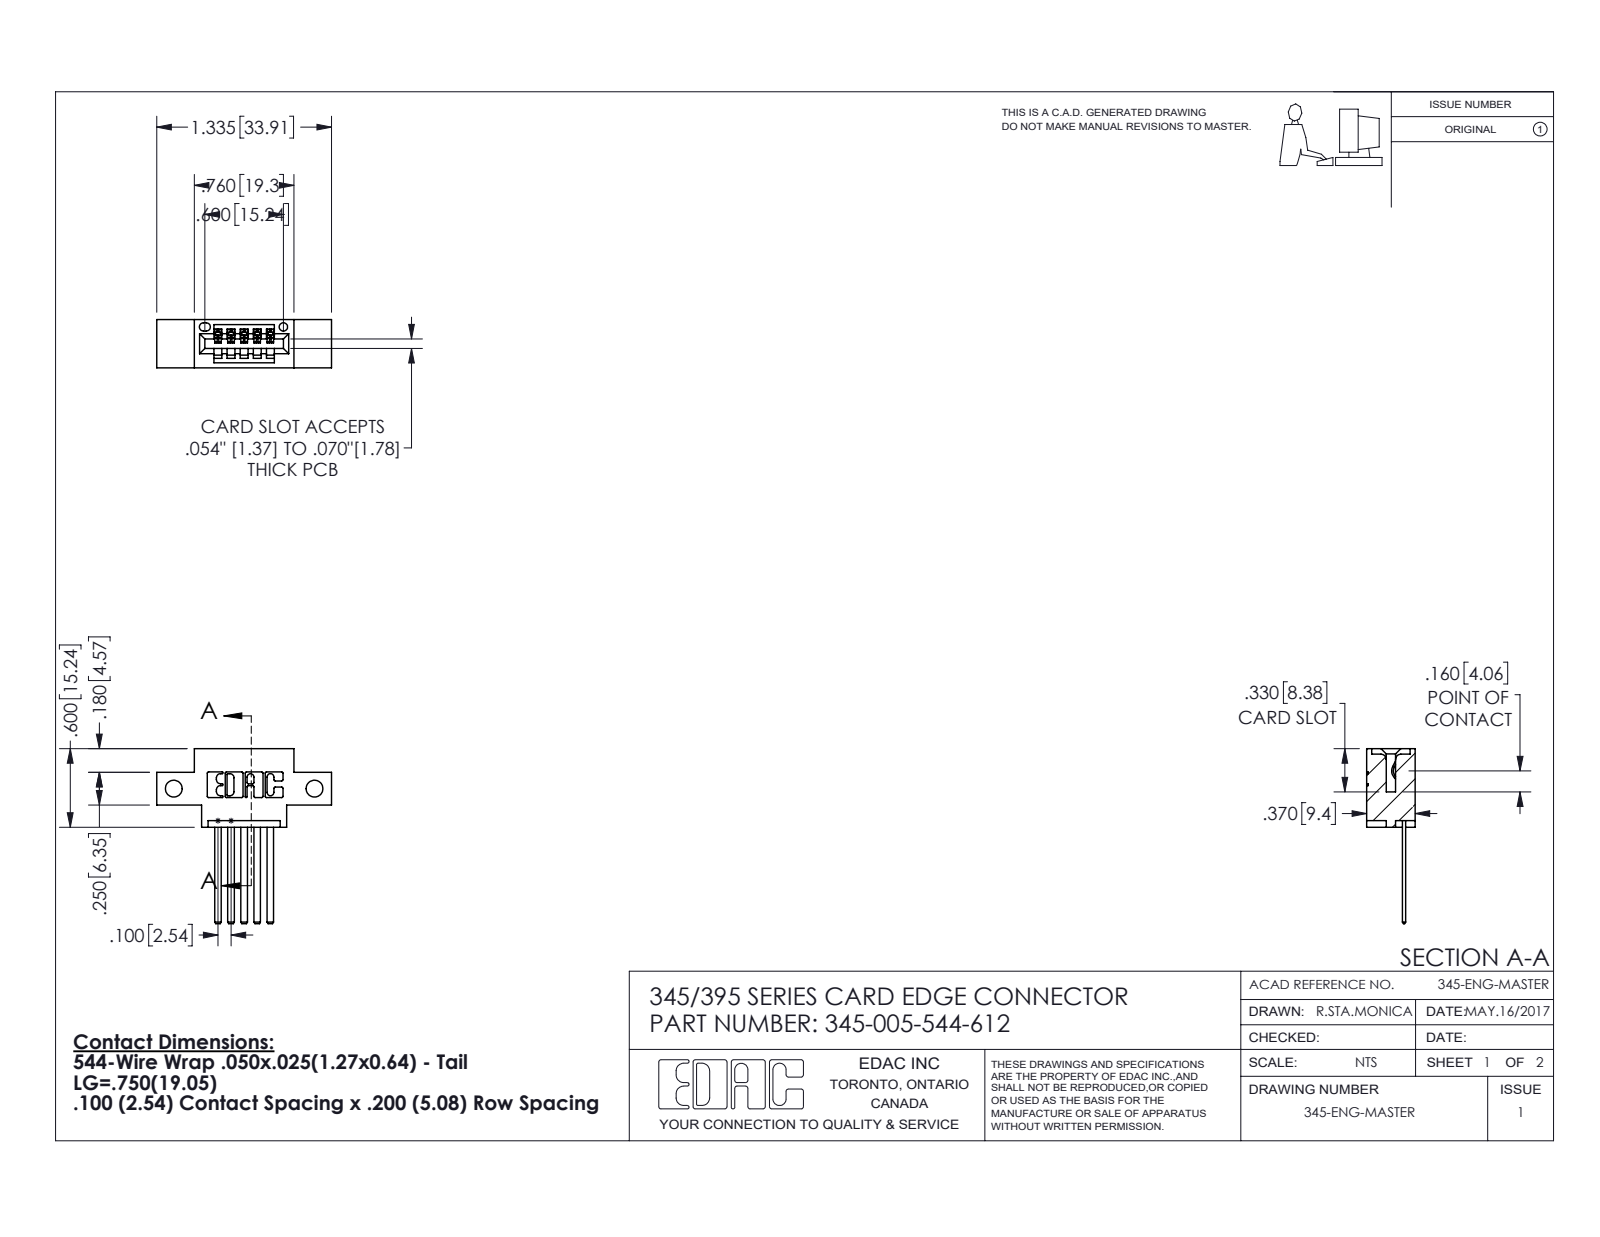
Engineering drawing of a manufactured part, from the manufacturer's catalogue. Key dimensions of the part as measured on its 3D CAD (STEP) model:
Part name (STEP PRODUCT): 345-005-544-612; 345 Part_0.170 Offset - Side Mount; 345-292-001_345-293-144
STEP written by: SolidWorks 2016 (CONFIG_CONTROL_DESIGN)
Units: inches
Bodies: 6 solids, 390 faces (264 planar, 126 cylindrical, 0 other)
Overall size (bounding box): 1.337 × 1.335 × 0.37
Volume: 0.169 in³ · Surface area: 5.182 in²
Round holes (diameter × count): ⌀0.128 ×2, ⌀0.064 ×1
Partial cylindrical surfaces — rounded edges, fillets, slot ends (radius × count): R0.01 ×22, R0.006 ×10, R0.007 ×6, R0.031 ×6, R0.026 ×3, R0.031 ×2, R0.04 ×2, R0.014 ×1
Main face-to-face distances: 0.37, 0.298, 0.072, 0.2, 0.1, 0.25, 0.098, 0.272, 0.025, 0.15
Hole centre spacings: 1.075
